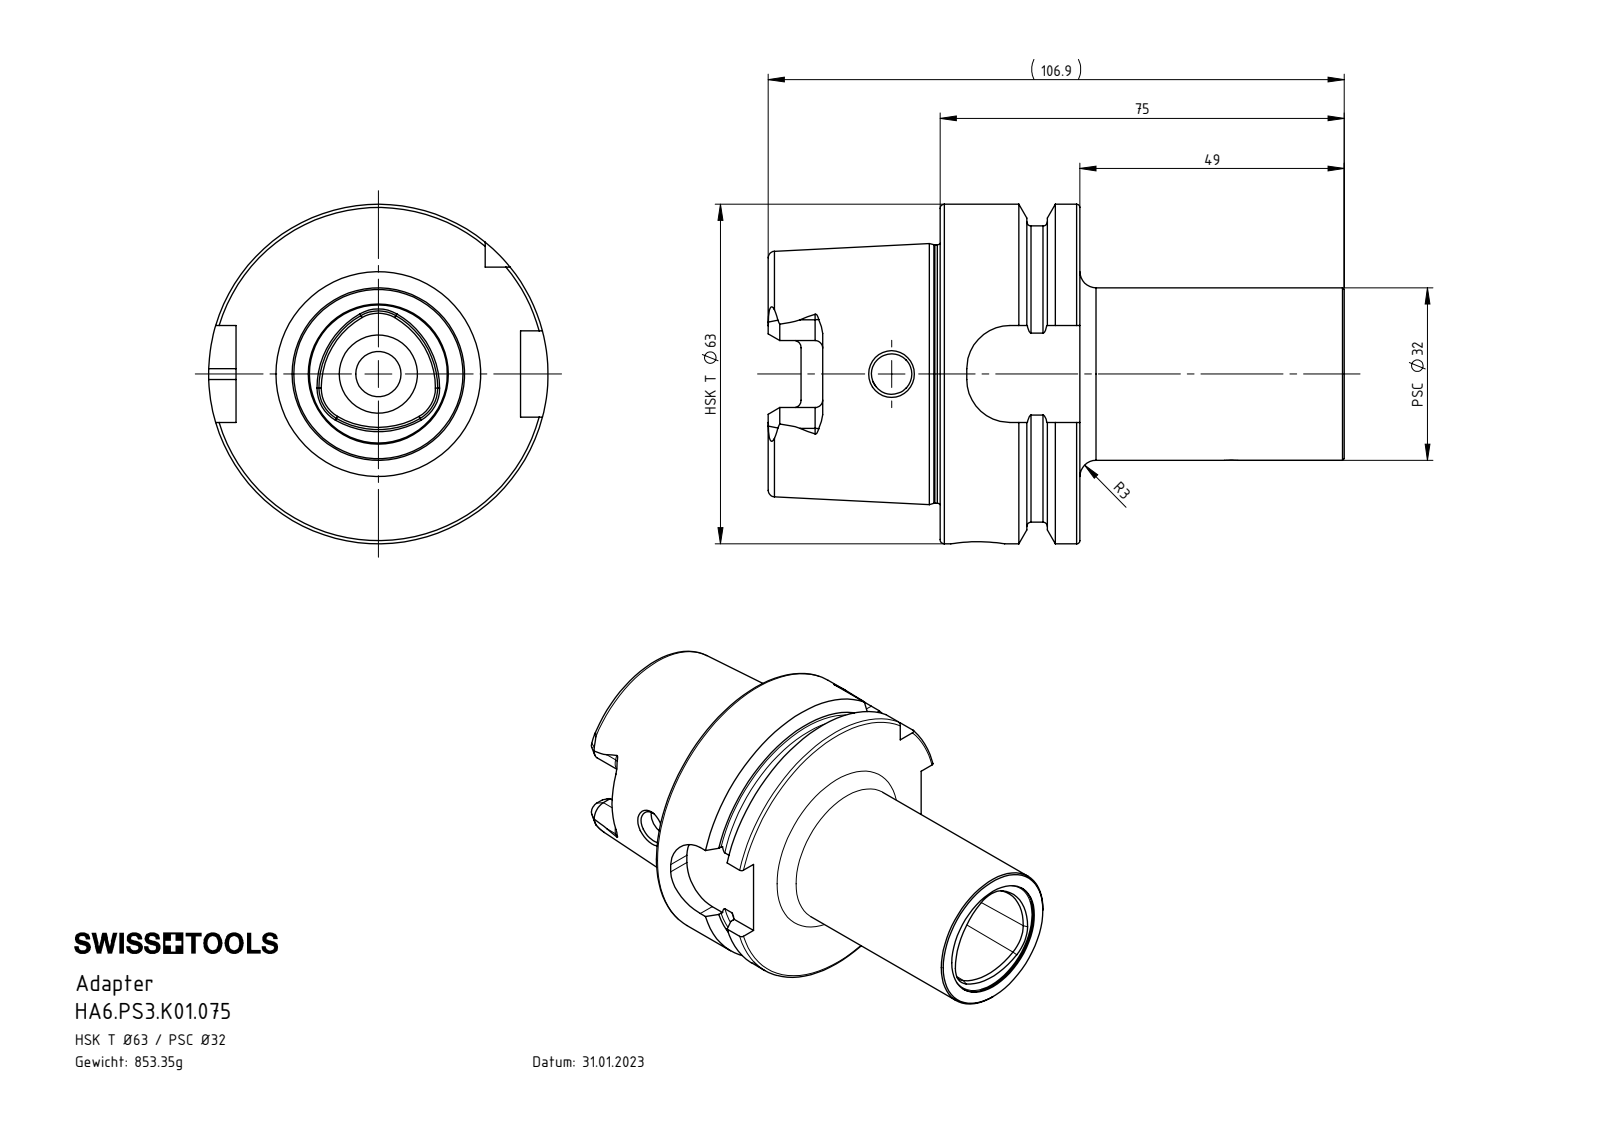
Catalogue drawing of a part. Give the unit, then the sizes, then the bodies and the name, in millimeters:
Units: millimetres
Overall size (bounding box): 106.9 × 63 × 63
Round holes (diameter × count): ⌀2.5 ×1, ⌀7.5 ×1, ⌀8.4 ×1, ⌀10 ×1, ⌀14.5 ×1, ⌀17 ×1, ⌀19 ×1, ⌀26 ×1, ⌀34 ×1, ⌀40 ×1
Round bosses / shafts (diameter × count): ⌀63 ×1, ⌀54.95 ×1, ⌀47.94 ×1, ⌀32 ×1
Partial cylindrical surfaces — rounded edges, fillets, slot ends (radius × count): R1.4 ×6, R2.88 ×4, R8 ×4, R6.28 ×3, R15.32 ×3
Main face-to-face distances: 25.95, 16, 9.95, 31.9, 41.85, 57.85, 52.8, 21.8, 11.85, 106.9
Hole centre spacings: 47
Volume: 108 705 mm³ · Surface area: 29 579 mm²
Bodies: 1 solid, 207 faces (49 planar, 57 cylindrical, 101 other)
Part name (STEP PRODUCT): HA6.PS3.K01.075
STEP written by: SolidWorks 2017 (AUTOMOTIVE_DESIGN)
